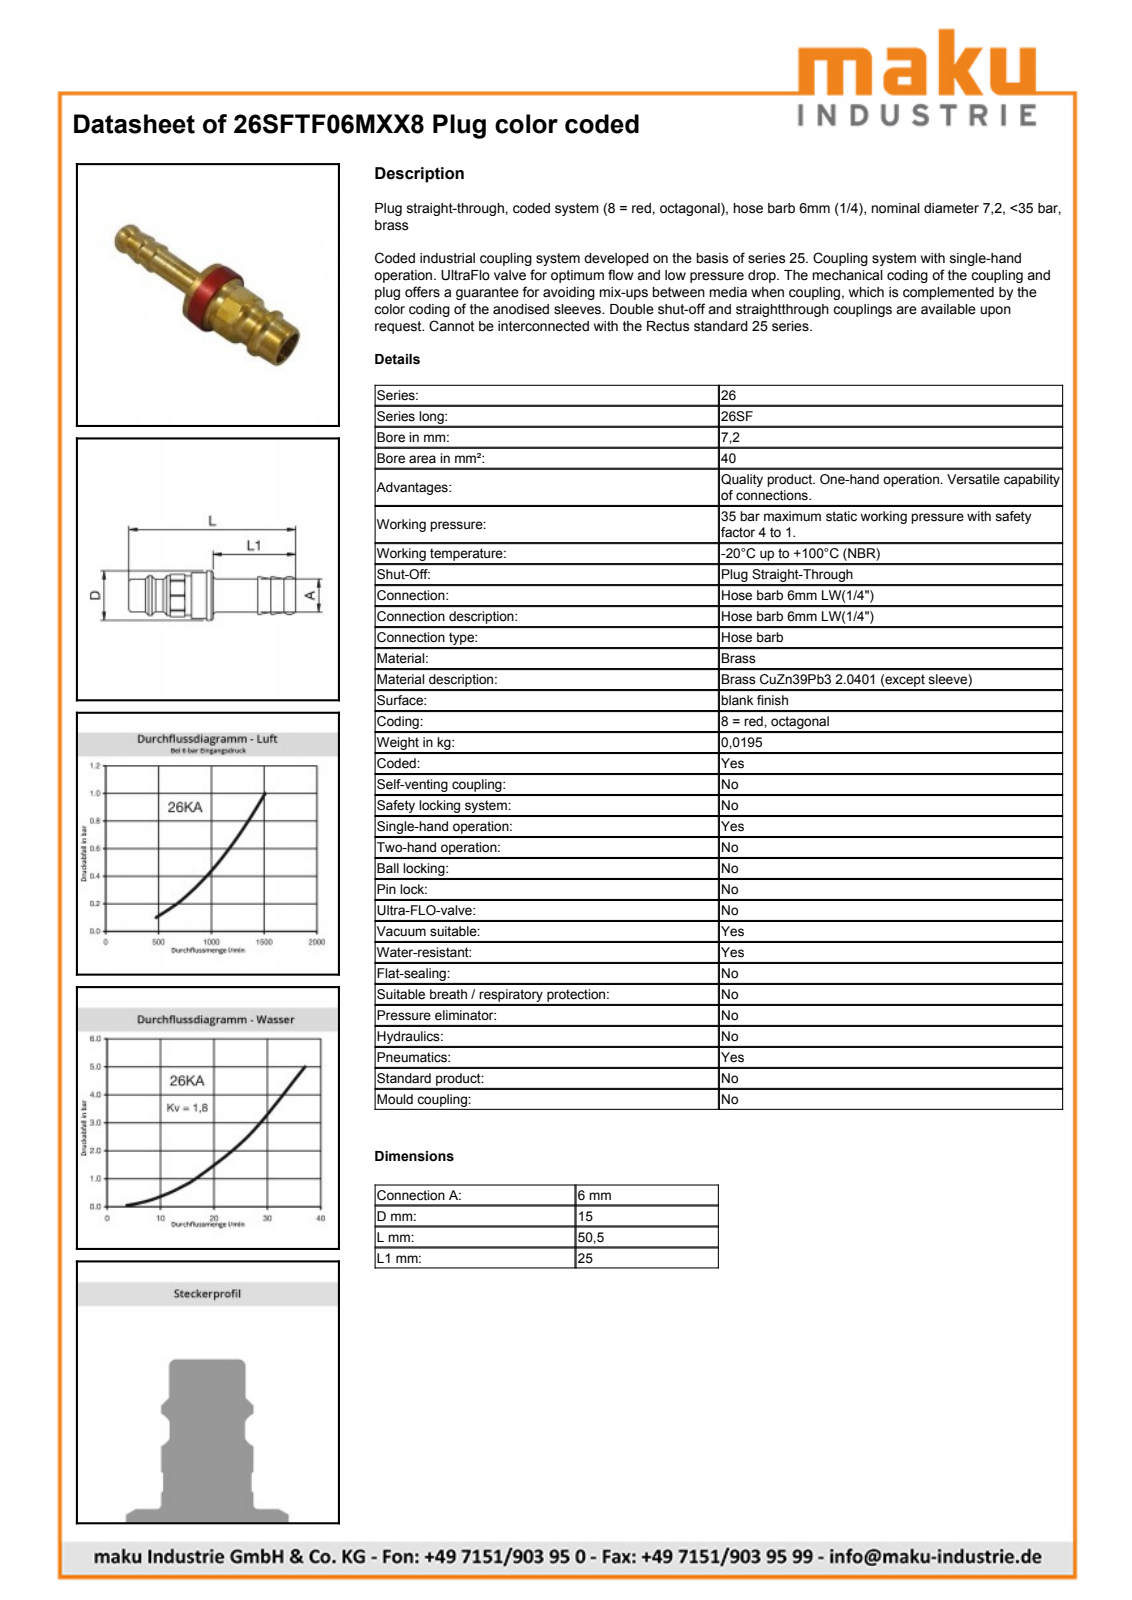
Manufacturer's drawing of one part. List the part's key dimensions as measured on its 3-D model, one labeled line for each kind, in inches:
Part name (STEP PRODUCT): D103821; D103817; D103012
STEP written by: Autodesk Inventor 2011 (AUTOMOTIVE_DESIGN)
Units: inches
Bodies: 2 solids, 71 faces (17 planar, 21 cylindrical, 33 other)
Overall size (bounding box): 1.988 × 0.61 × 0.61
Volume: 0.145 in³ · Surface area: 4.893 in²
Round holes (diameter × count): ⌀0.161 ×1, ⌀0.309 ×1, ⌀0.545 ×1, ⌀0.553 ×1
Round bosses / shafts (diameter × count): ⌀0.61 ×1, ⌀0.591 ×1, ⌀0.551 ×1, ⌀0.472 ×1, ⌀0.469 ×1, ⌀0.394 ×1, ⌀0.384 ×1, ⌀0.24 ×1
Partial cylindrical surfaces — rounded edges, fillets, slot ends (radius × count): R0.252 ×1
Main face-to-face distances: 0.472, 0.079, 0.256, 0.177, 0.244, 0.165, 0.984, 1.063, 1.228, 1.24
